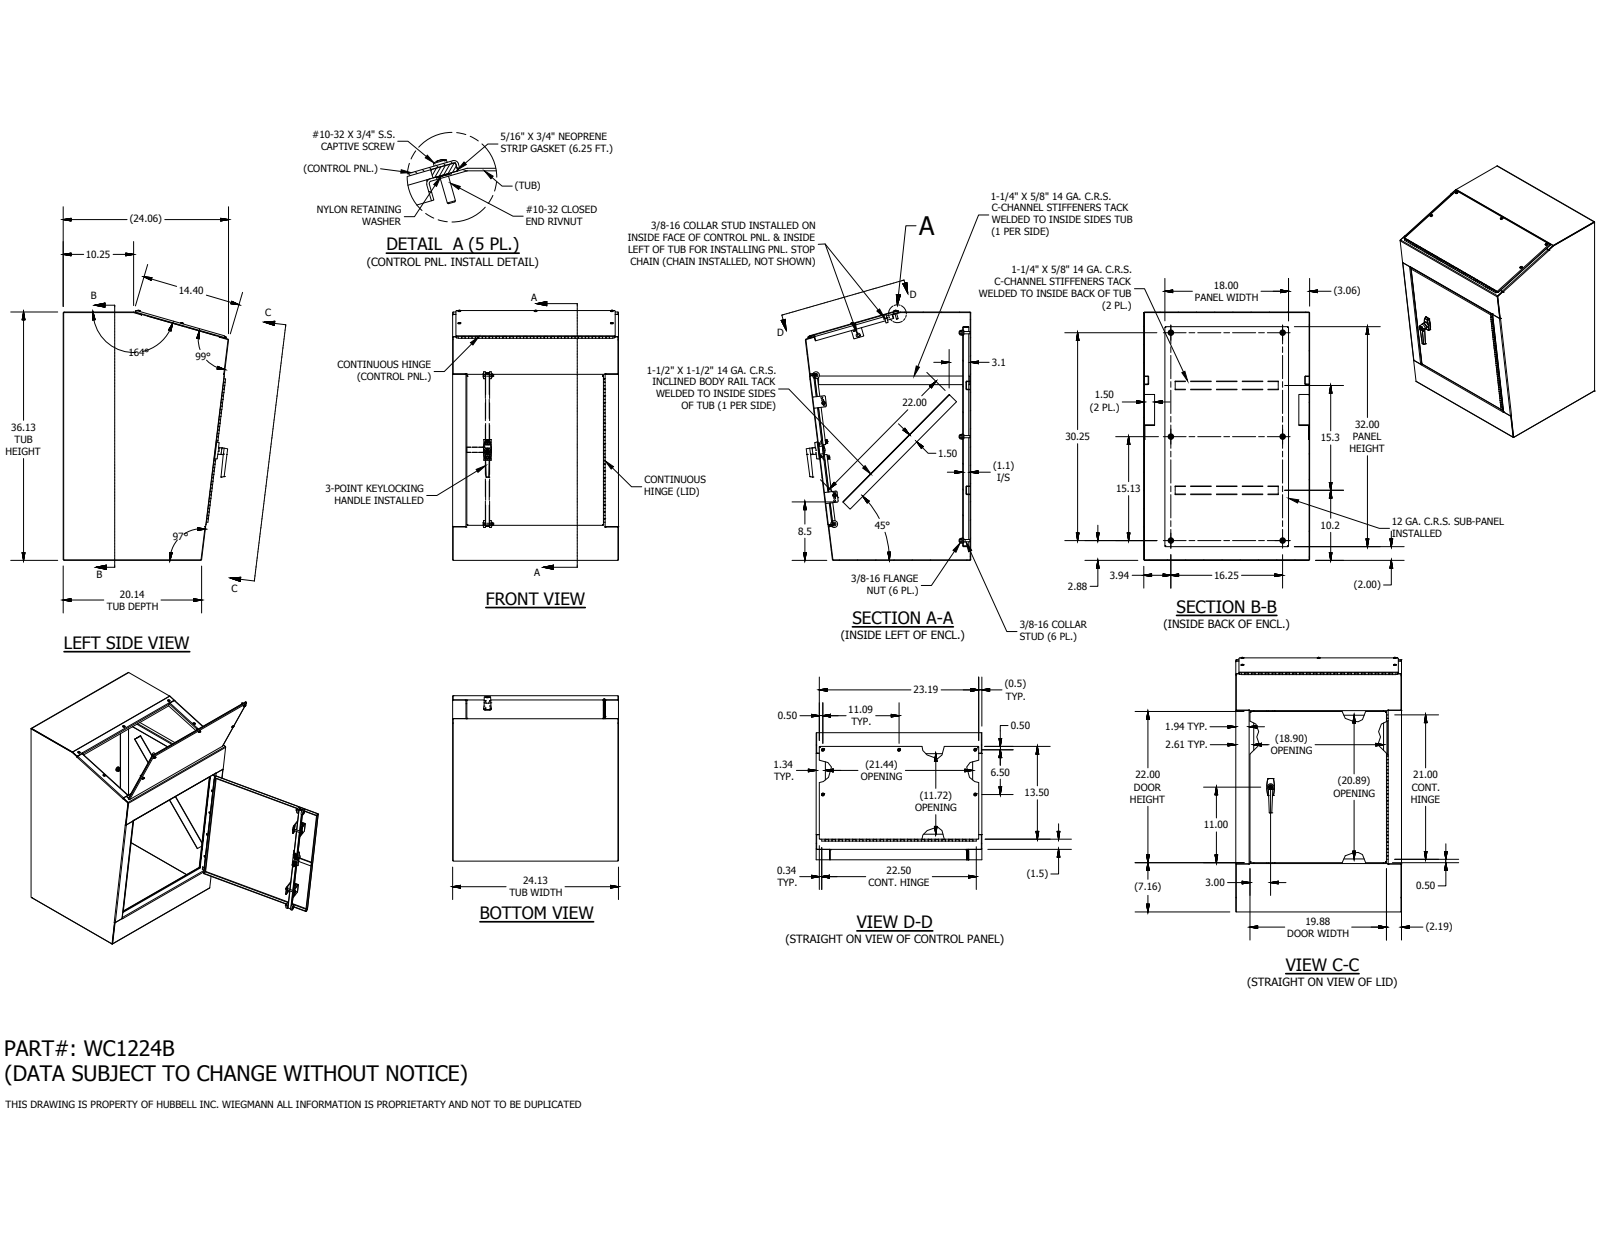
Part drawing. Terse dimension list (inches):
name: WC1224B
written by: SolidWorks 2019 (AUTOMOTIVE_DESIGN)
unit: in
bodies: 77 solids, 2661 faces (1502 planar, 731 cylindrical, 428 other)
size: 36.379 × 24.125 × 24.061
volume: 449 in³; area: 11 614 in²
holes: 10× ⌀0.313, 8× ⌀0.277, 7× ⌀0.25, 6× ⌀0.307, 6× ⌀0.563, 5× ⌀0.083, 5× ⌀0.156, 5× ⌀0.196, 5× ⌀0.257, 5× ⌀0.278, 4× ⌀0.2, 3× ⌀0.138
bosses: 8× ⌀0.33, 7× ⌀0.625, 7× ⌀0.157, 5× ⌀0.453, 5× ⌀0.406, 5× ⌀0.248, 5× ⌀0.167, 4× ⌀0.533
rounds: 28× R0.136, 25× R0.008, 18× R0.062, 16× R0.025, 16× R0.031, 14× R0.063, 10× R0.105, 8× R0.03
face distances: 0.074, 24.051, 23.977, 24.125, 0.094, 1, 1.094, 1.074, 1.168, 36.051
hole spacings: 1.154, 0.906, 1.159, 11.094, 15.125, 22.187, 22.2, 0.875
